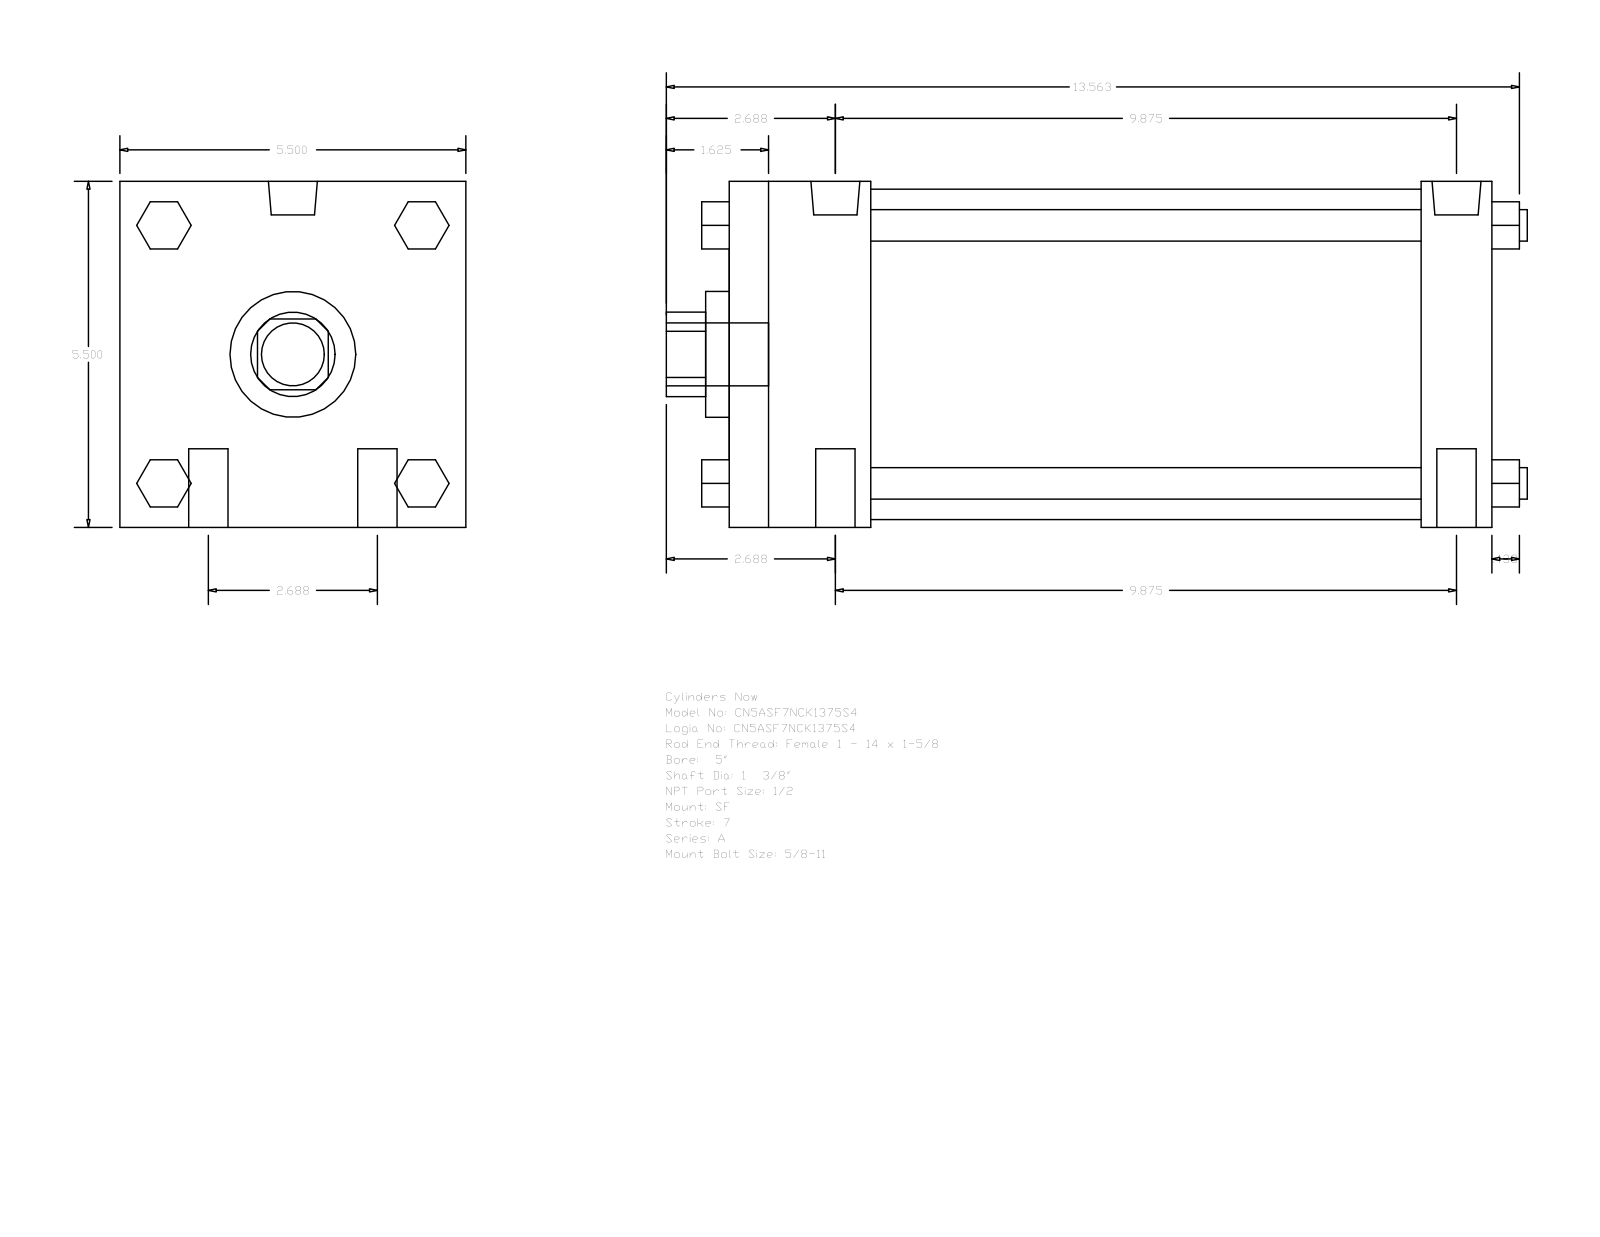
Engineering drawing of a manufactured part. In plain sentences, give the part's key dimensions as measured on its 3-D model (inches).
The part is named "A_SF__0500_1.375". Its 3-D file was written by "GSSL Pune (CONFIG_CONTROL_DESIGN)". It is 0 solids with 124 faces: 94 planar, 30 cylindrical and 0 other. Overall it measures 13.687 by 5.5 by 5.5 inches. Round holes: 1 of diameter 1.375, 1 of diameter 2, 1 of diameter 5.25. Round bosses or shafts: 4 of diameter 0.625, 4 of diameter 0.5, 2 of diameter 0.778, 2 of diameter 0.344, 1 of diameter 1. Partial cylindrical surfaces (rounded edges, fillets, slot ends): 1 of radius 0.672. The main face-to-face distances are 5.5, 12.125, 1.125, 2.25, 11, 8.75, 9.875, 0.75, 2.05, 3.55.
